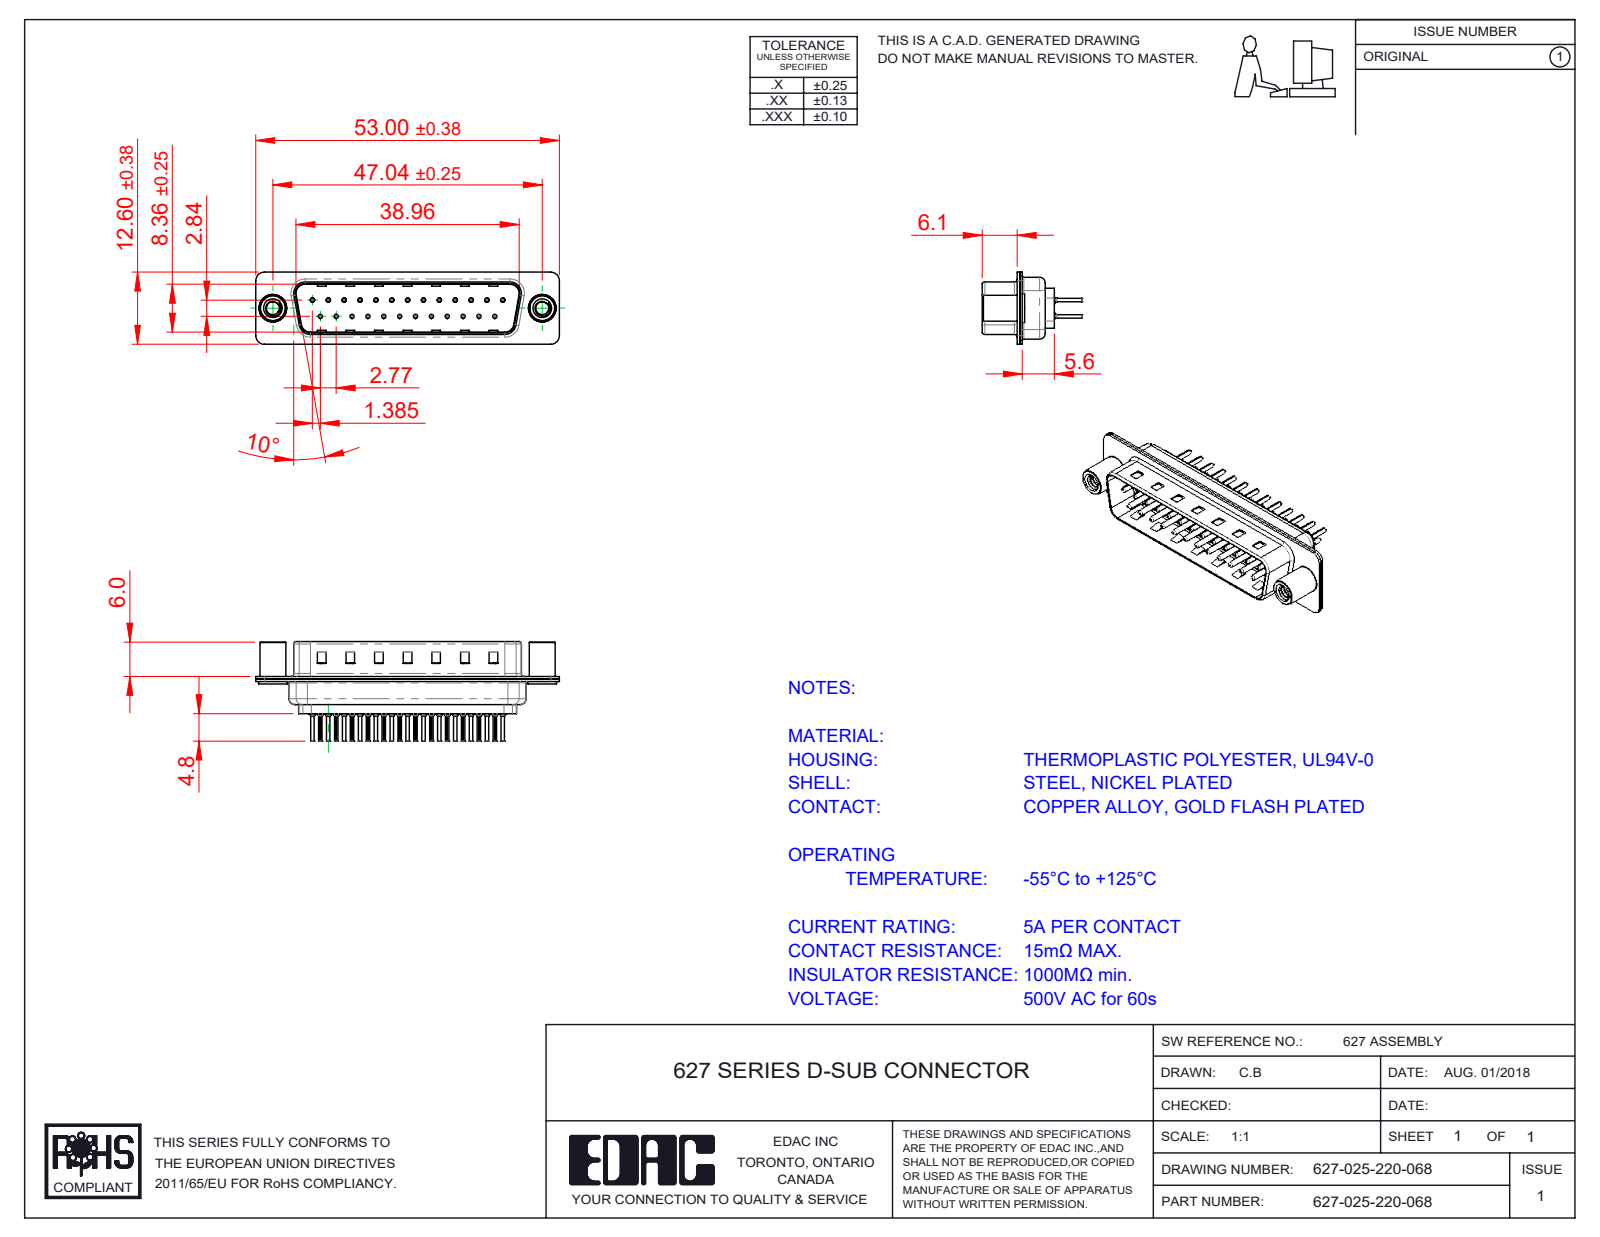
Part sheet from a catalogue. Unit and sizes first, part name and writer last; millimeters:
Units: millimetres
Overall size (bounding box): 53 × 17.3 × 12.6
Round holes (diameter × count): ⌀0.2 ×25, ⌀0.35 ×25, ⌀1.1 ×25, ⌀1.6 ×25, ⌀2.26 ×2, ⌀4 ×2, ⌀4.8 ×2
Round bosses / shafts (diameter × count): ⌀2 ×25, ⌀1.5 ×25, ⌀0.75 ×25, ⌀0.6 ×25, ⌀5 ×2, ⌀4.9 ×2, ⌀4.5 ×2
Partial cylindrical surfaces — rounded edges, fillets, slot ends (radius × count): R0.1 ×50, R1.5 ×16, R2 ×12, R0.5 ×8, R1.6 ×8, R0.25 ×4, R0.6 ×4, R0.65 ×4
Main face-to-face distances: 0.4, 0.45, 0.82, 9.58, 0.9, 8.76, 1.5, 1.4, 6.5, 6.05
Hole centre spacings: 3.16, 8.31, 2.77, 5.54, 11.08, 16.62, 5.03, 5.04
Volume: 2 746 mm³ · Surface area: 7 999 mm²
Bodies: 30 solids, 2860 faces (773 planar, 1090 cylindrical, 997 other)
Part name (STEP PRODUCT): 627 Shell Front_25 Contacts; 627 Shell Rear_25 Contacts; 627 Housing_25 LP; 627 Contact Row 1_20L (+3 more)
STEP written by: SolidWorks 2020 (CONFIG_CONTROL_DESIGN)
